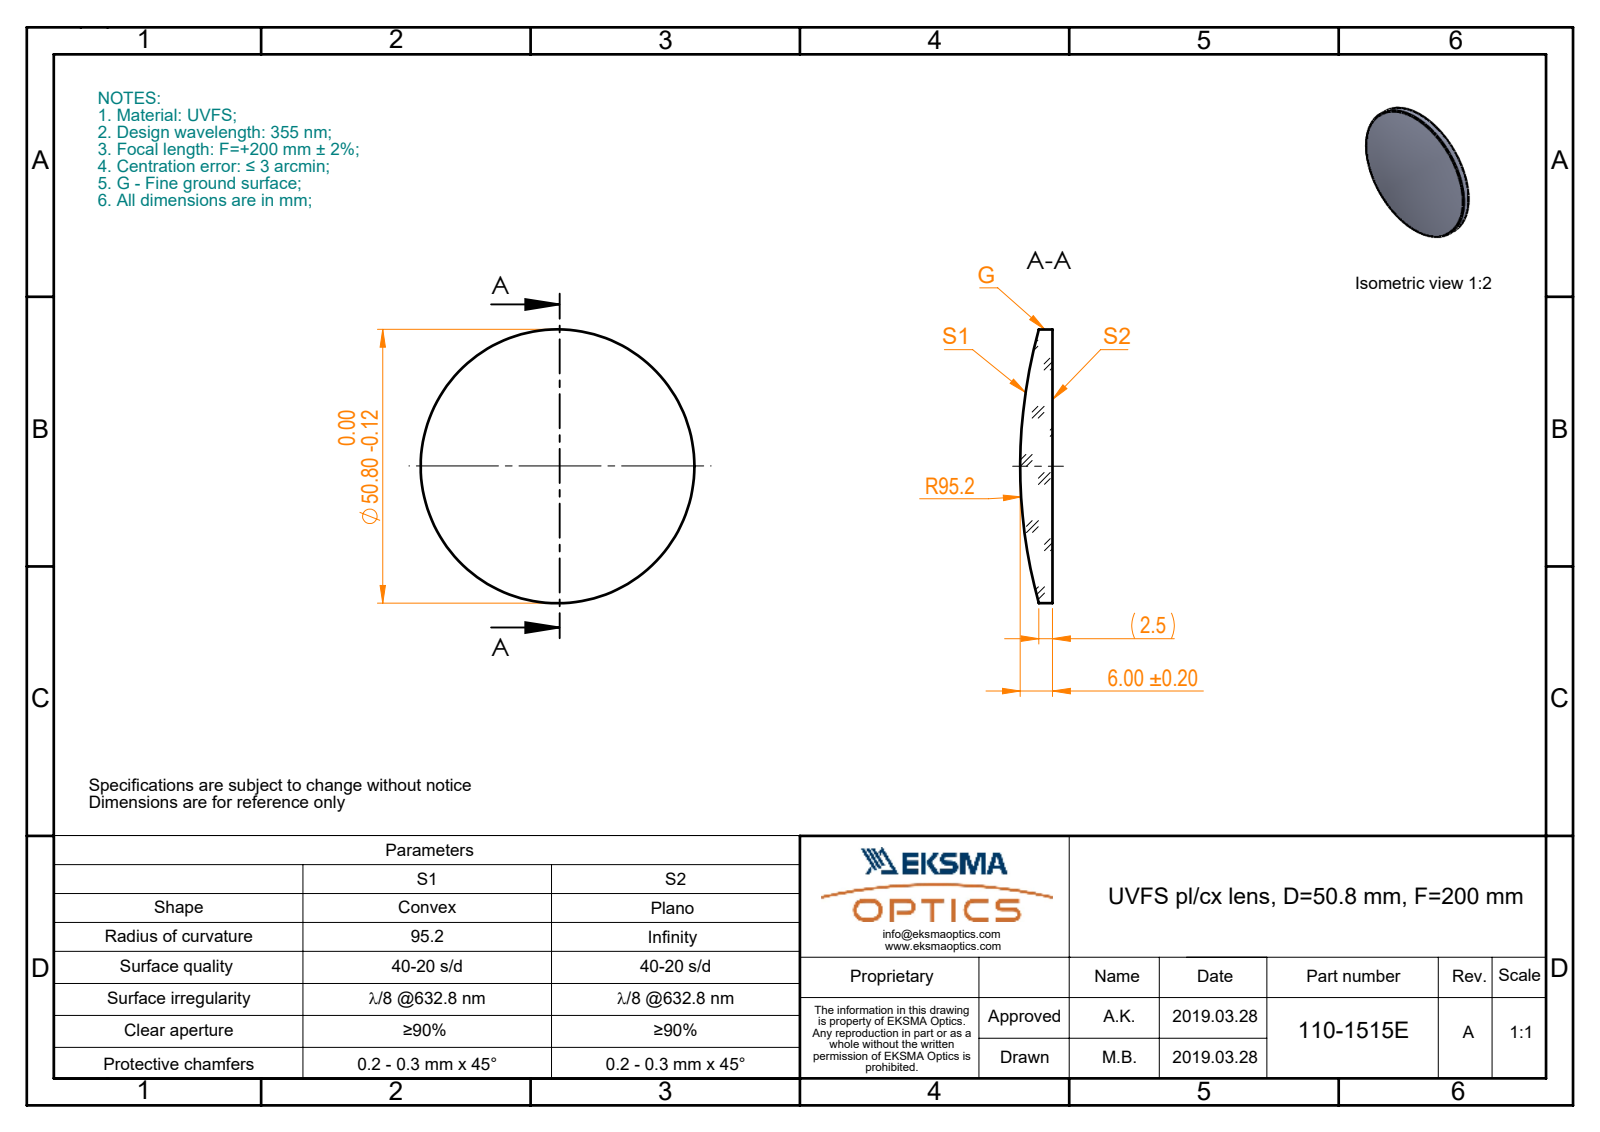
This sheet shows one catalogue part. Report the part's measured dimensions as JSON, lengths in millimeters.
{"part_name": "110-1515E UVFS pl-cx 50.8 F200", "step_written_by": "SolidWorks 2017 (CONFIG_CONTROL_DESIGN)", "units": "millimeters", "bodies": {"solids": 1, "faces": 5, "planar": 1, "cylindrical": 2, "other": 2}, "overall_size": [50.8, 50.8, 6], "volume_mm3": 8686, "surface_area_mm2": 4498, "round_bosses_or_shafts": [[50.8, 1]]}
